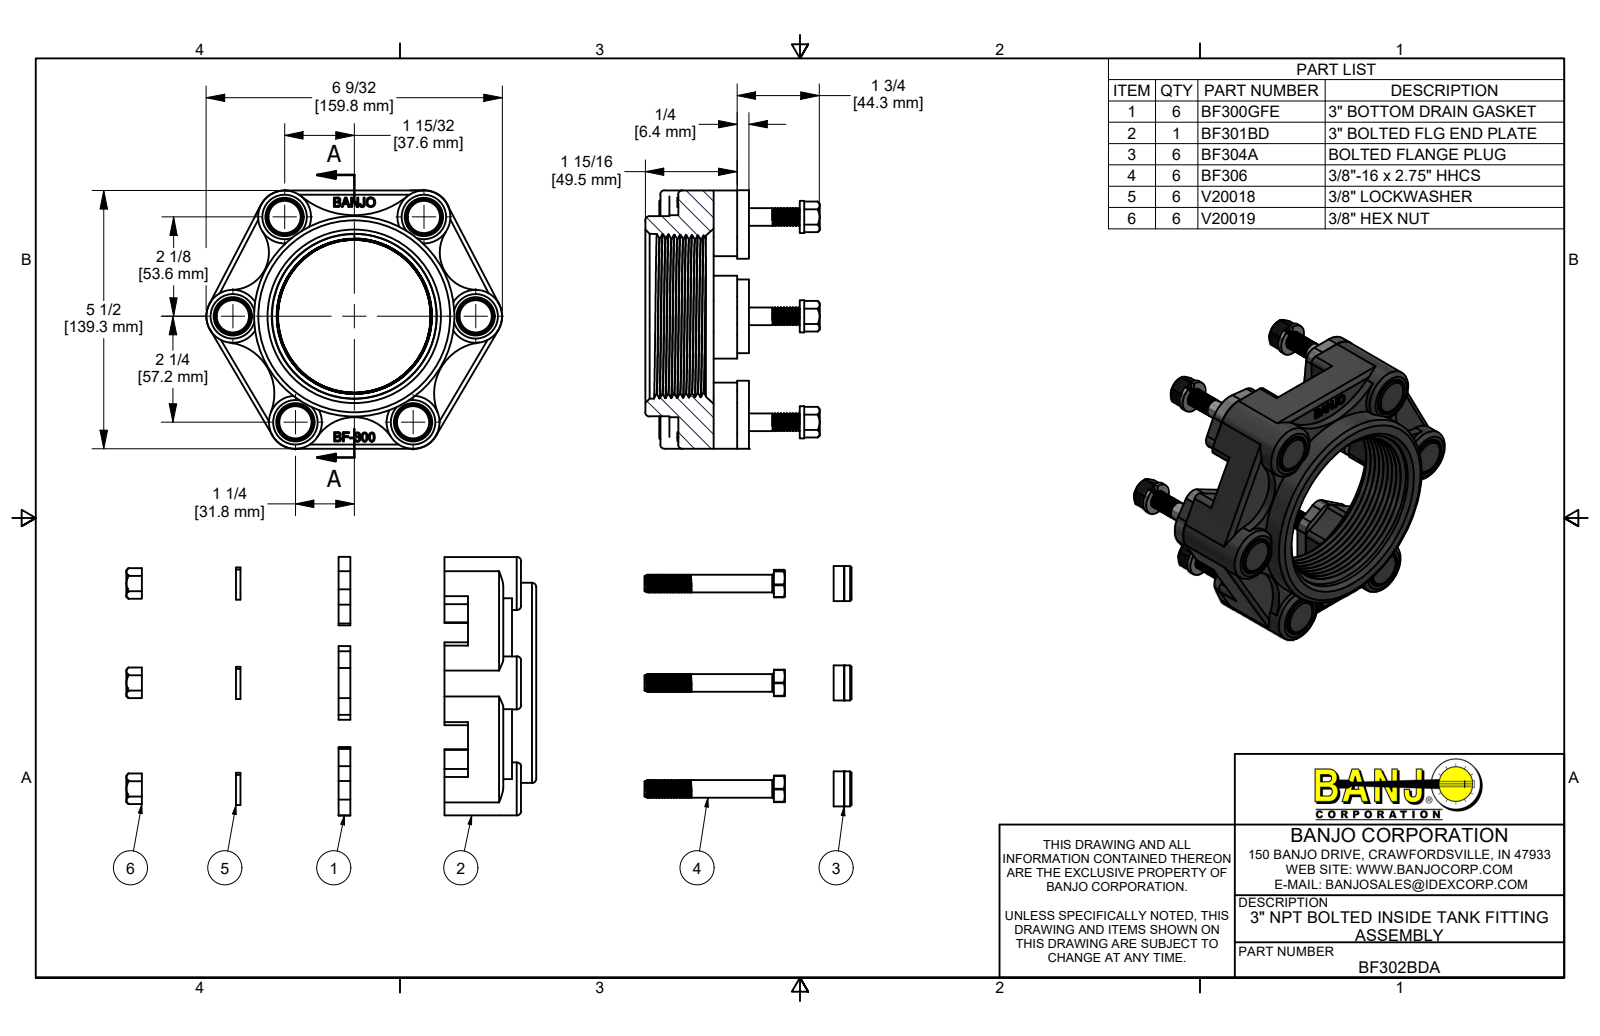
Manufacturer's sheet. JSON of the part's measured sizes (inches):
{"part_name": "BF302BDA; BF301BD; BF304A; BF306 (+3 more)", "step_written_by": "Autodesk Inventor 2019 (AUTOMOTIVE_DESIGN)", "units": "inches", "bodies": {"solids": 31, "faces": 1513, "planar": 486, "cylindrical": 487, "other": 540}, "overall_size": [6.293, 5.491, 3.707], "volume_in3": 27.6, "surface_area_in2": 193.1, "round_holes": [[0.307, 6], [0.385, 6], [0.406, 6], [0.41, 6], [0.715, 6], [0.75, 6]], "round_bosses_or_shafts": [[0.324, 90], [1.125, 6], [0.742, 6], [0.687, 6], [0.375, 6], [4.25, 1]], "partial_cylinders_radius": [[0.125, 24], [0.25, 24], [0.162, 12], [0.09, 6], [0.32, 6], [0.56, 6], [1.71, 6], [0.794, 2]], "face_to_face_distances": [0.75, 0.25, 0.5, 1.25, 1.5, 1.25, 0.5, 0.25, 0.023, 0.773], "hole_center_spacings": [2.38, 2.614, 4.366, 4.442, 4.575, 5.144, 2.5, 2.96]}
